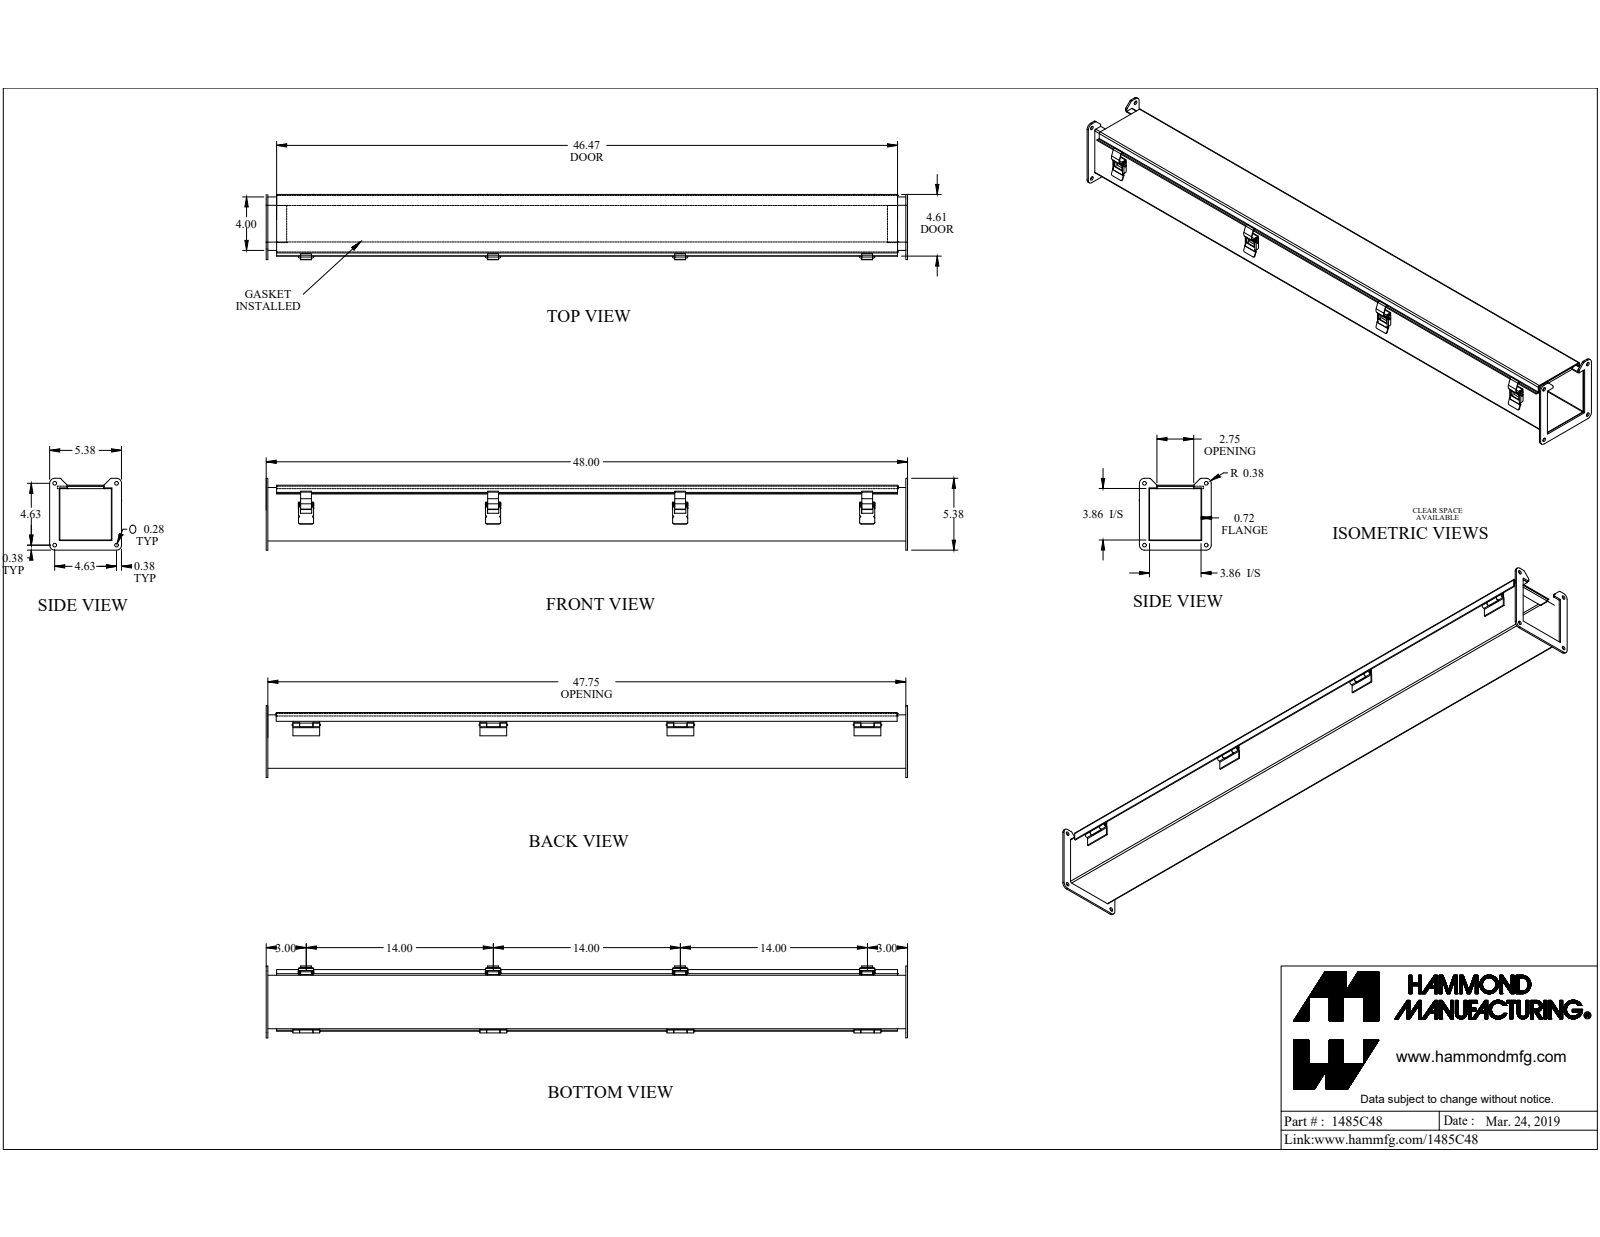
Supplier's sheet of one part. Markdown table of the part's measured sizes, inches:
| quantity | value |
| --- | --- |
| part name | 1485C48 |
| STEP written by | SolidWorks 2019 (CONFIG_CONTROL_DESIGN) |
| units | inches |
| bodies | 32 solids, 700 faces (418 planar, 274 cylindrical, 8 other) |
| overall size | 48 × 5.383 × 5.375 |
| volume | 81.95 in³ |
| surface area | 2 089 in² |
| round holes (diameter × count) | 0.281 × 4, 0.125 × 1, 0.13 × 1, 0.164 × 1 |
| round bosses / shafts (diameter × count) | 0.187 × 2, 0.275 × 1, 0.156 × 1, 0.125 × 1 |
| partial cylindrical surfaces (radius × count) | 0.016 × 25, 0.125 × 13, 0.035 × 9, 0.039 × 9, 0.076 × 9, 0.015 × 8, 0.029 × 8, 0.086 × 8 |
| main face-to-face distances | 0.072, 3.928, 4.1, 4, 3.856, 4.172, 4.028, 0.172, 3.913, 3.841 |
| hole center spacings | 4.625, 6.541, 0.285, 1.075, 1.57, 1.849, 2.785, 3.057 |
